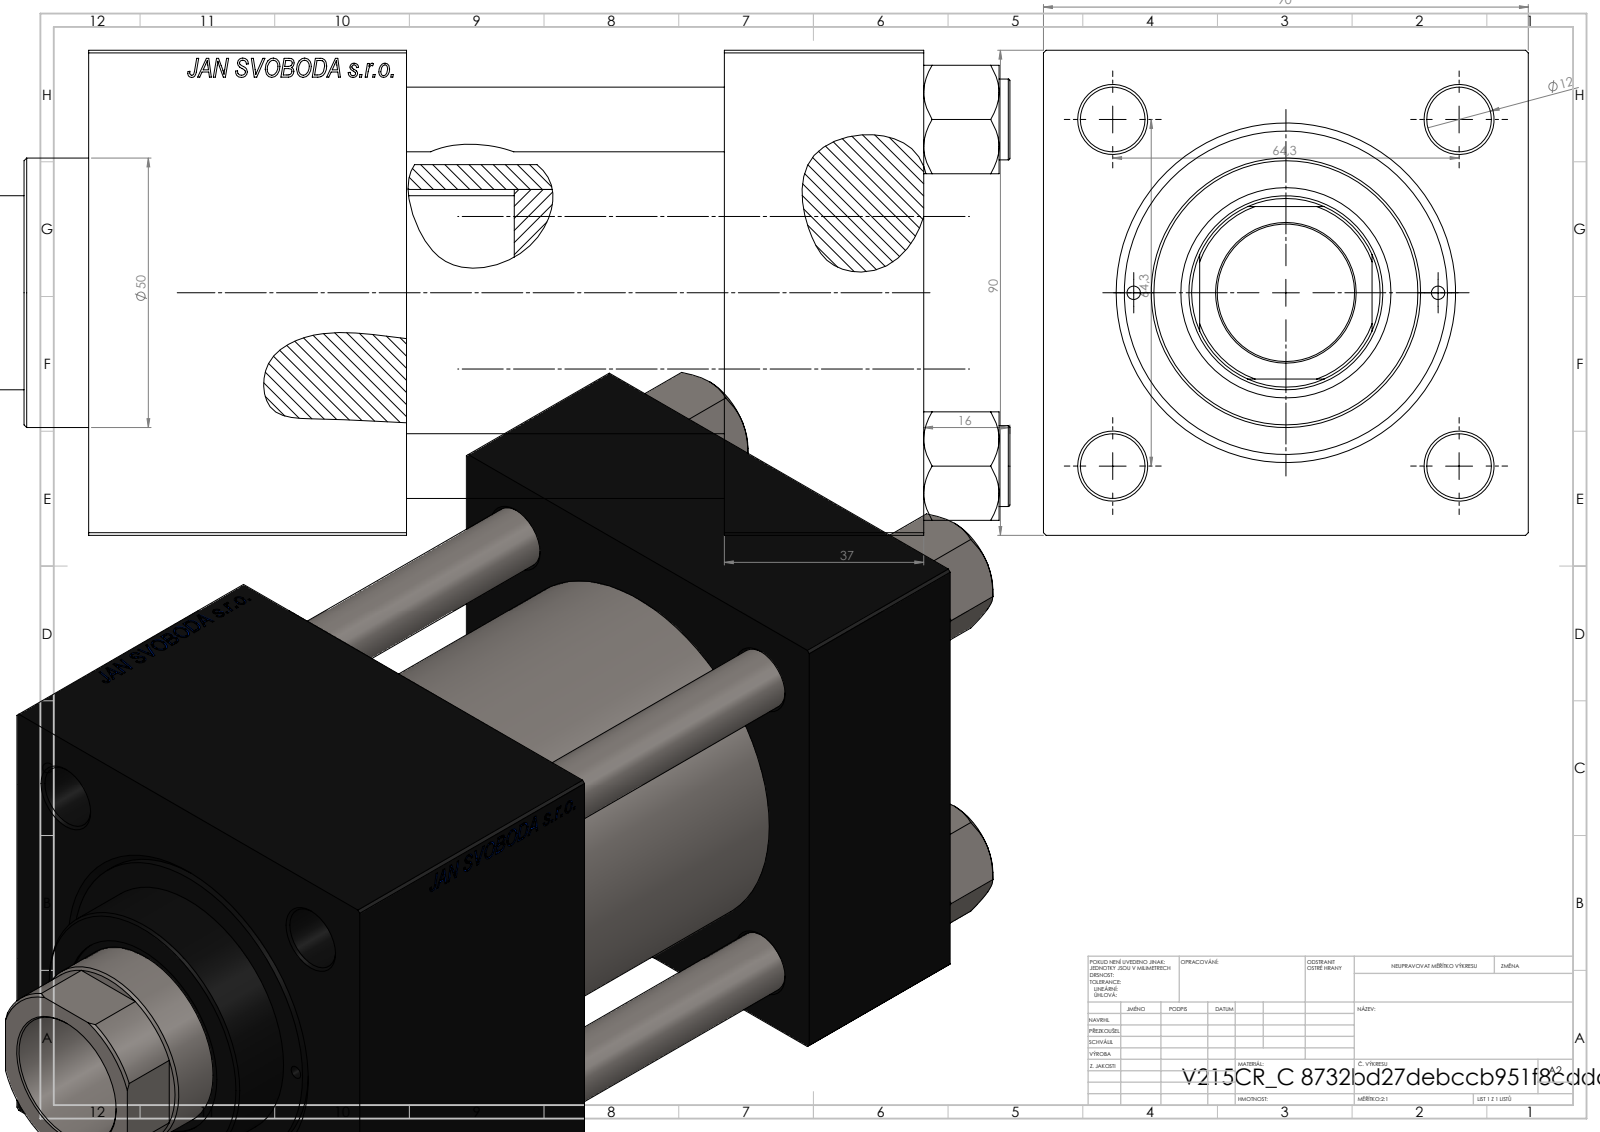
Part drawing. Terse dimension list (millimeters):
name: NUT_M5_C; V215CR_VCP_C; V215_VC_A; V215CR_C_Body (+1 more)
written by: SolidWorks 2019 (CONFIG_CONTROL_DESIGN)
unit: mm
bodies: 11 solids, 1154 faces (528 planar, 90 cylindrical, 536 other)
size: 203 × 90 × 90
volume: 967 907 mm³; area: 184 311 mm²
holes: 4× ⌀12, 2× ⌀2.5, 2× ⌀7, 2× ⌀20.96, 2× ⌀30, 1× ⌀25.5, 1× ⌀36, 1× ⌀39, 1× ⌀50, 1× ⌀60, 1× ⌀63
bosses: 4× ⌀15, 1× ⌀69
rounds: 1× R17.5
face distances: 90, 59, 37, 155, 118, 96, 126.3, 89.3, 30.3, 28.7
hole spacings: 32.39, 45.47, 64.3, 68.42, 28.25, 90.93, 56.5, 97.5
